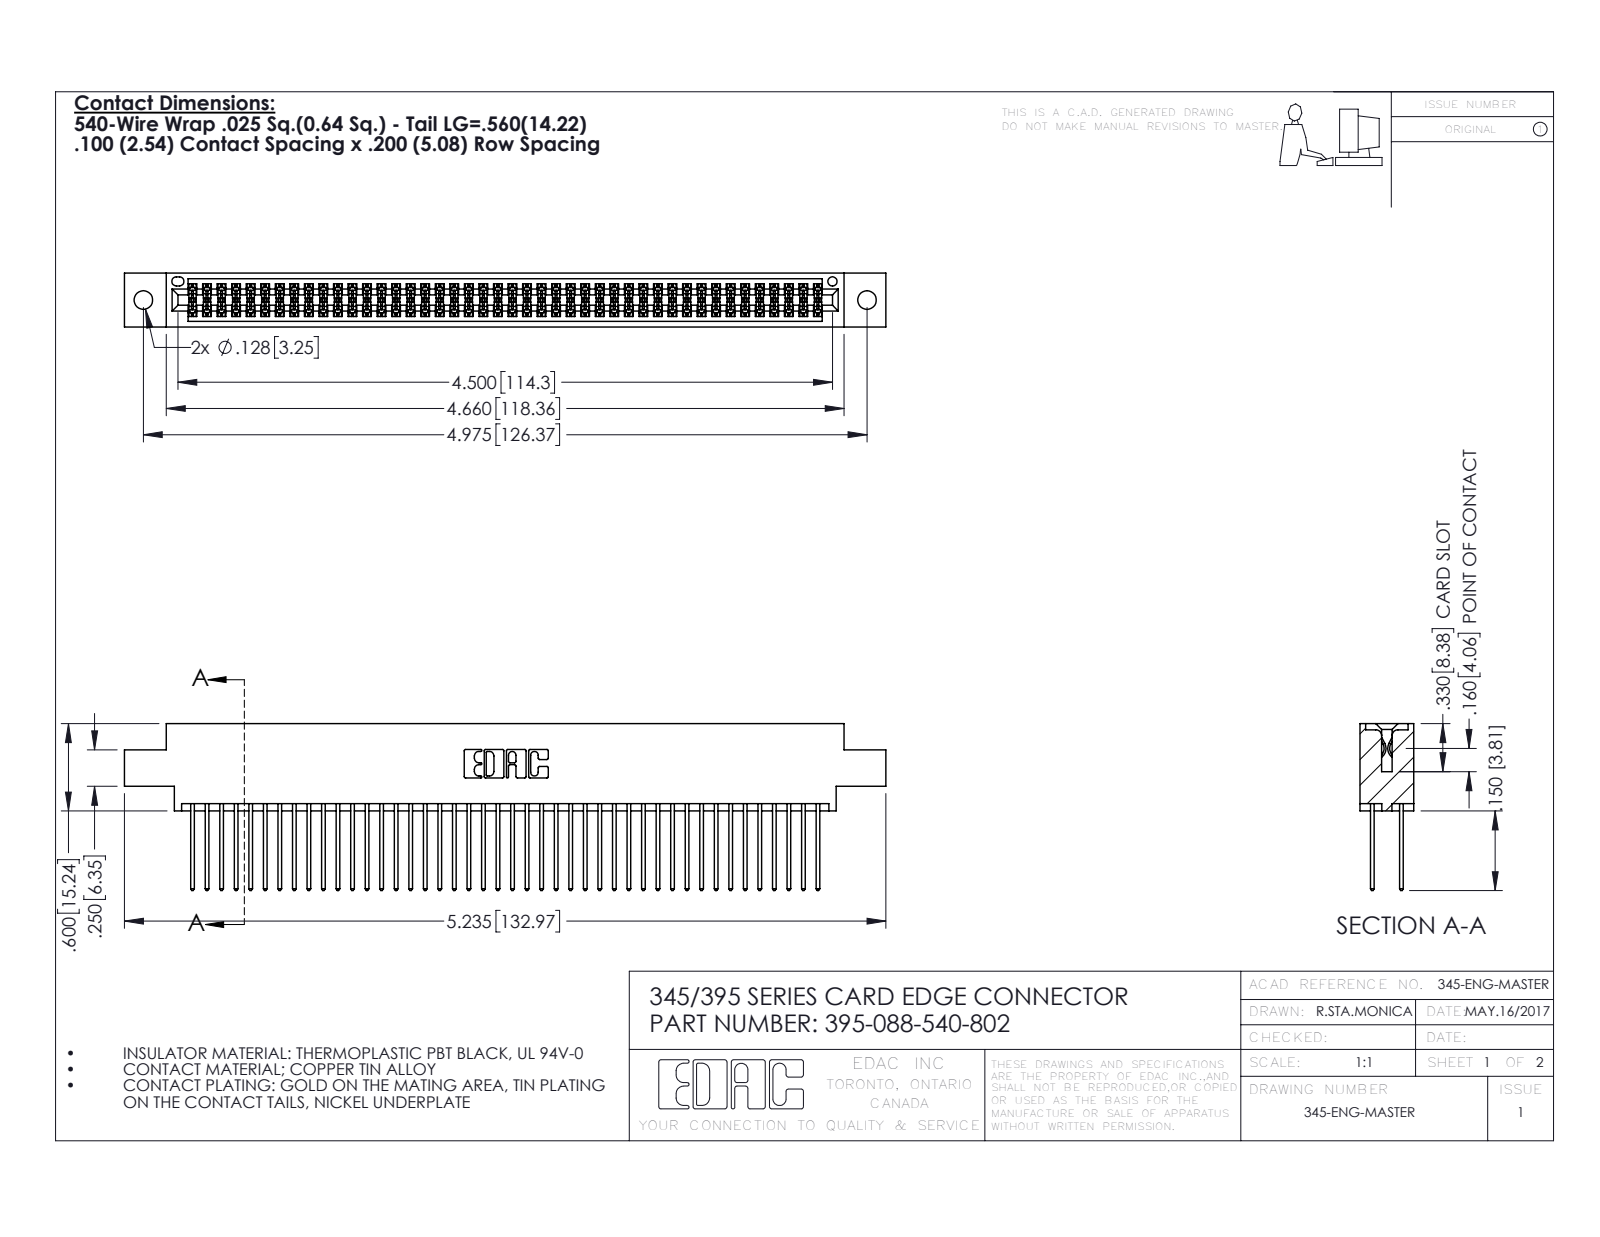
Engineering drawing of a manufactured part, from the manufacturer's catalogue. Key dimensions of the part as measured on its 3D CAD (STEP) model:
Part name (STEP PRODUCT): 395-088-540-802; 345-292-001_345-293-140; 345 Part_0.170 Offset - 0.128 Dia
STEP written by: SolidWorks 2016 (CONFIG_CONTROL_DESIGN)
Units: inches
Bodies: 89 solids, 4530 faces (2988 planar, 1542 cylindrical, 0 other)
Overall size (bounding box): 5.235 × 1.147 × 0.37
Volume: 0.801 in³ · Surface area: 32.32 in²
Round holes (diameter × count): ⌀0.128 ×2, ⌀0.064 ×1
Partial cylindrical surfaces — rounded edges, fillets, slot ends (radius × count): R0.006 ×132, R0.01 ×88, R0.01 ×22, R0.007 ×6, R0.031 ×6, R0.026 ×3, R0.014 ×2, R0.019 ×2
Main face-to-face distances: 0.298, 0.072, 0.2, 0.098, 0.272, 0.025, 0.37, 0.225, 0.175, 0.149
Hole centre spacings: 0.27, 4.739, 4.975
